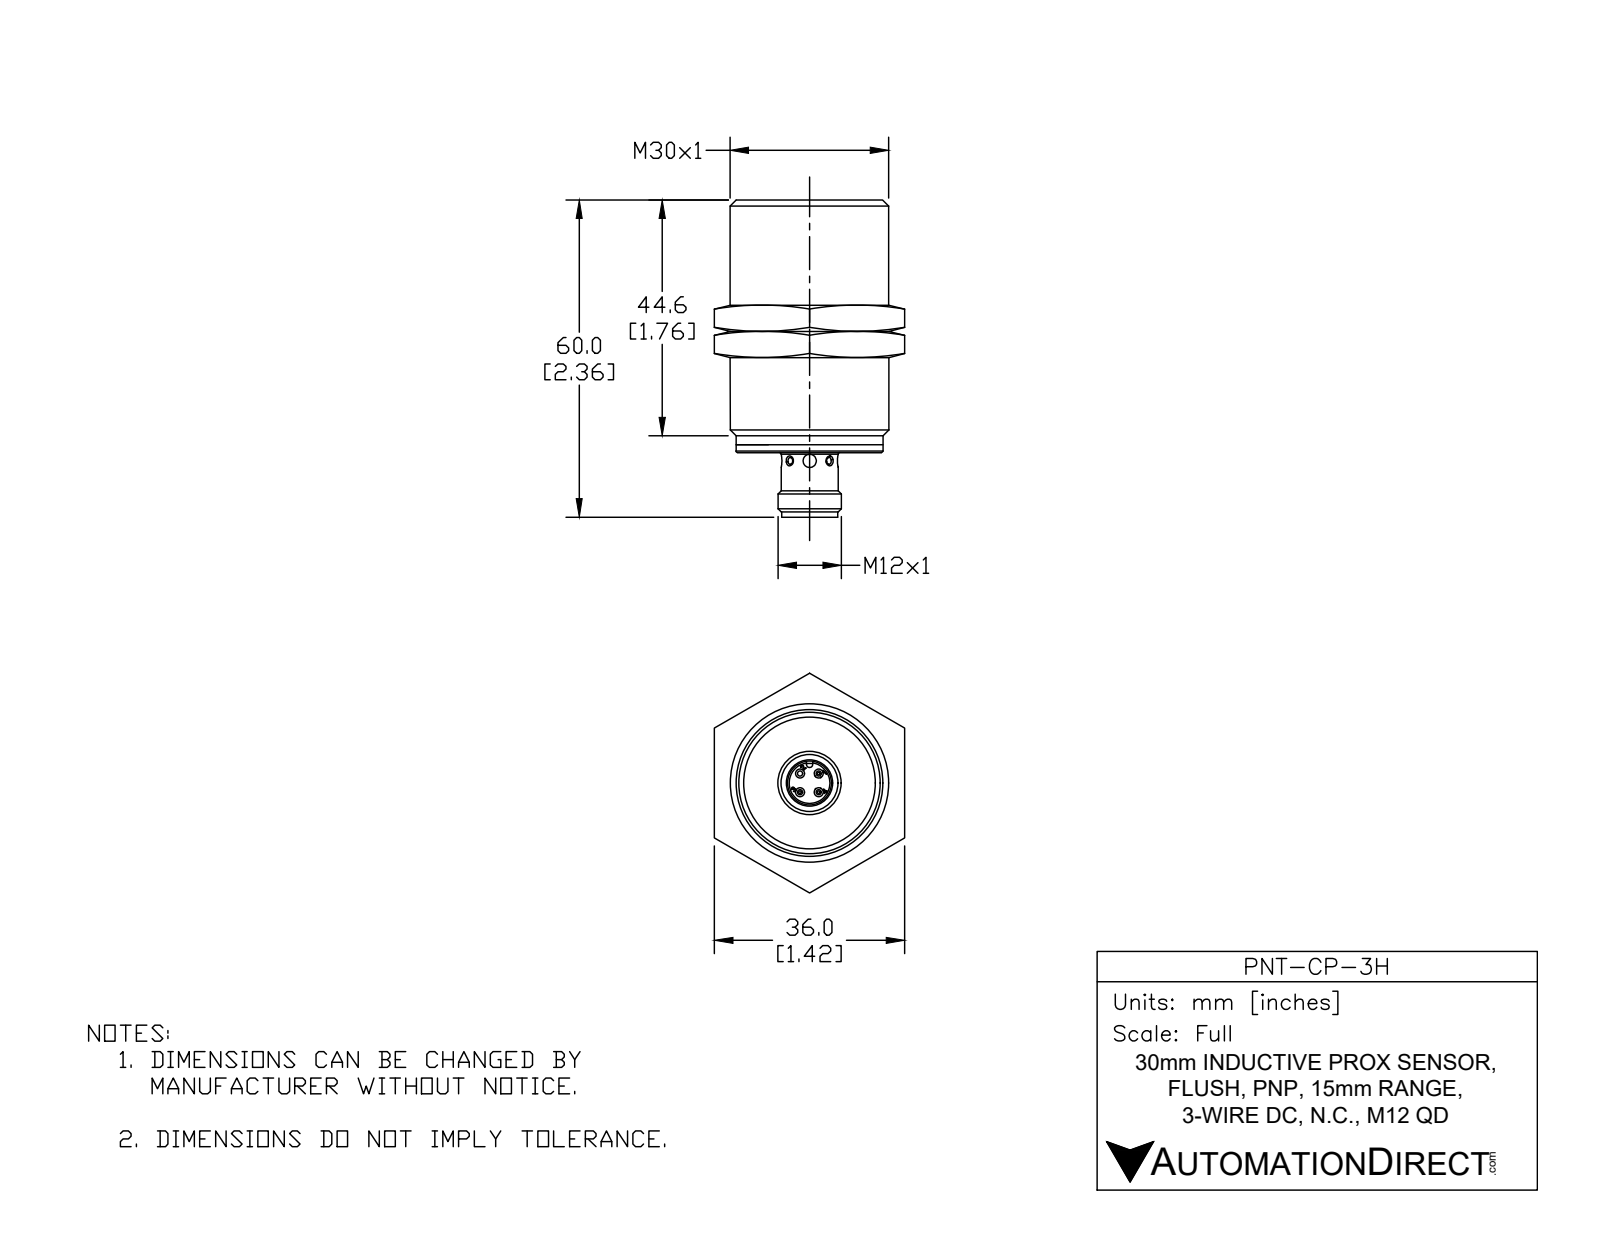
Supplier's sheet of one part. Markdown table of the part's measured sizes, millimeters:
| quantity | value |
| --- | --- |
| part name | PNT-CP-3H |
| STEP written by | SolidWorks 2017 (AUTOMOTIVE_DESIGN) |
| units | millimeters |
| bodies | 1 solid, 660 faces (260 planar, 164 cylindrical, 236 other) |
| overall size | 60 × 30 × 30 |
| volume | 31 690 mm³ |
| surface area | 16 240 mm² |
| round holes (diameter × count) | 1.1 × 3, 1 × 2, 2.5 × 2, 1 × 1, 1 × 1, 8.2 × 1, 8.3 × 1, 10 × 1, 26.6 × 1, 27.3 × 1 |
| round bosses / shafts (diameter × count) | 1 × 9, 30 × 1, 27.8 × 1, 27.5 × 1, 27.3 × 1, 26.5 × 1, 26.3 × 1, 25.9 × 1 |
| partial cylindrical surfaces (radius × count) | 0.1 × 12, 0.5 × 8, 4 × 6, 0.8 × 3, 1 × 3, 0.6 × 1, 0.8 × 1 |
| main face-to-face distances | 4, 47.8, 43.8, 0.9, 3, 46.8, 47.1, 3.3, 0.8, 0.7 |
| hole center spacings | 2.5, 3.5, 5 |
